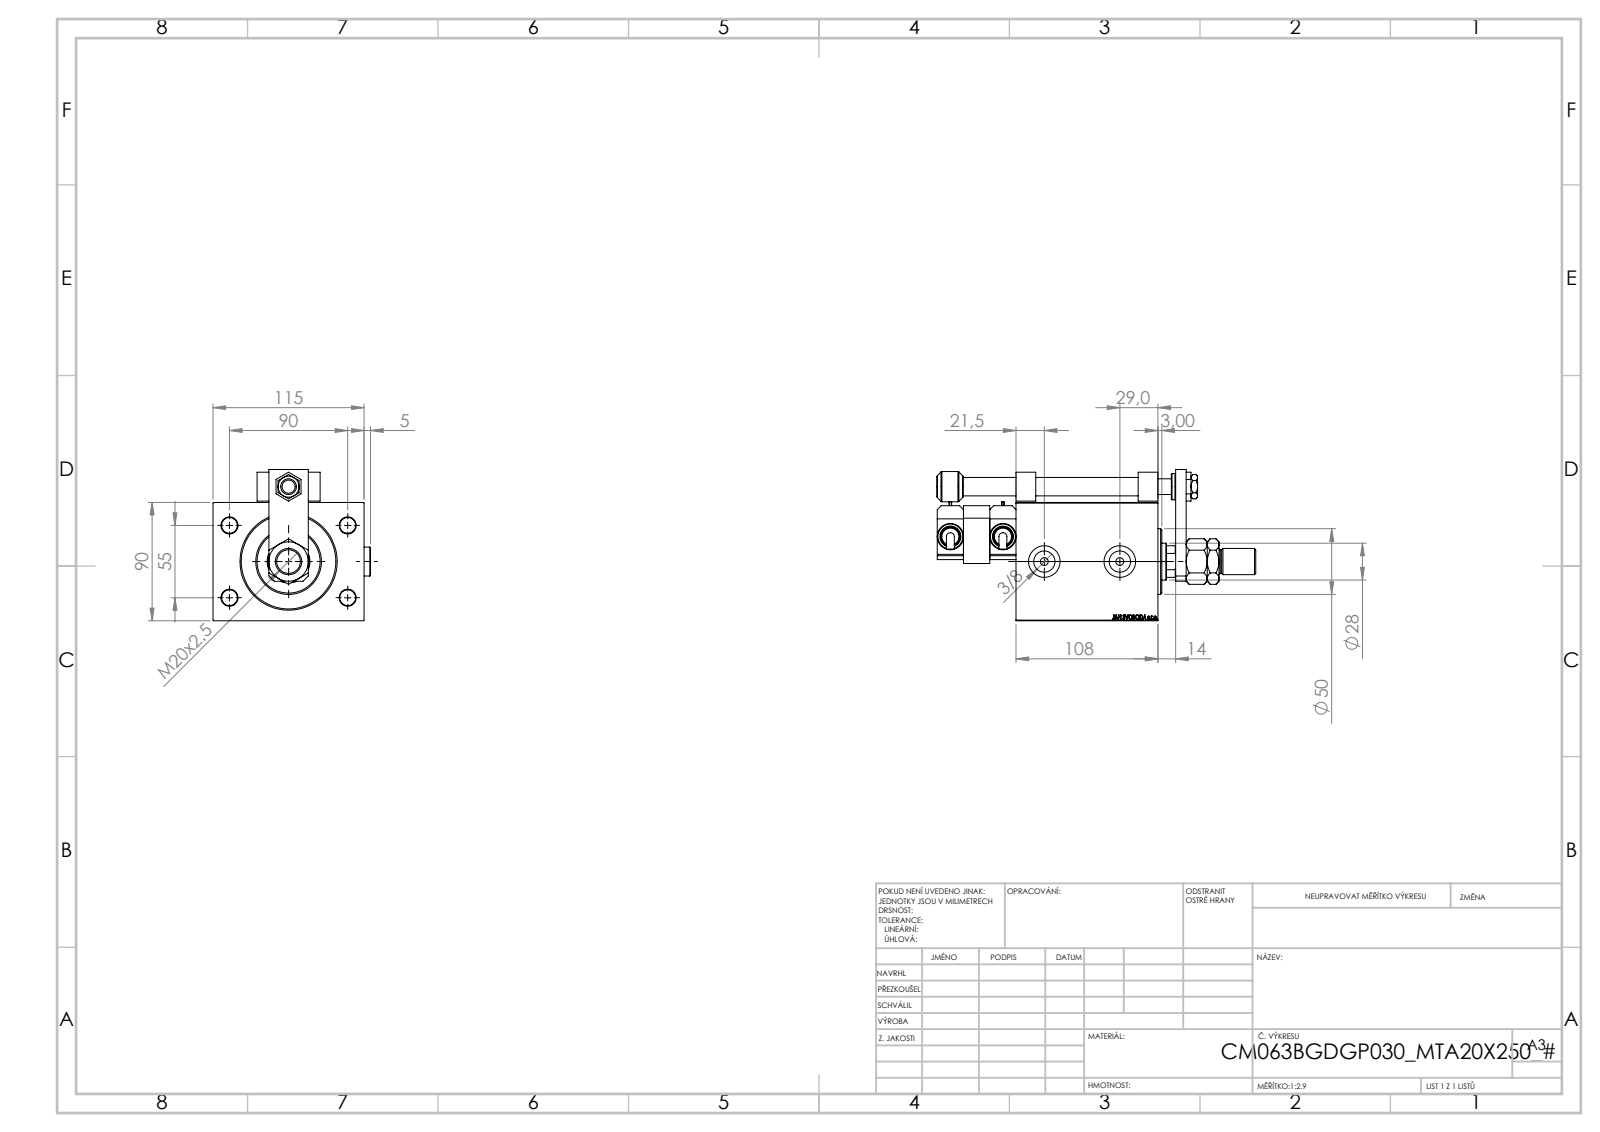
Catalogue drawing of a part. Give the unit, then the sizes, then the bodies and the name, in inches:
Units: inches
Overall size (bounding box): 9.559 × 4.72 × 4.528
Round holes (diameter × count): ⌀0.472 ×5, ⌀0.157 ×4, ⌀0.315 ×4, ⌀0.236 ×2, ⌀0.637 ×2, ⌀0.945 ×2, ⌀0.512 ×1, ⌀0.551 ×1, ⌀0.728 ×1, ⌀0.787 ×1, ⌀1.102 ×1, ⌀1.24 ×1
Round bosses / shafts (diameter × count): ⌀0.787 ×3, ⌀0.866 ×2, ⌀0.63 ×2, ⌀0.551 ×2, ⌀0.236 ×2, ⌀1.969 ×1, ⌀0.906 ×1, ⌀0.709 ×1
Partial cylindrical surfaces — rounded edges, fillets, slot ends (radius × count): R0.118 ×1, R0.531 ×1
Main face-to-face distances: 3.543, 4.528, 4.252, 0.787, 0.689, 1.476, 3.563, 1.378, 1.575, 0.531
Hole centre spacings: 2.076, 0.787, 2.119, 2.165, 3.543, 3.661, 3.745, 3.769
Volume: 74.57 in³ · Surface area: 286.5 in²
Bodies: 17 solids, 1212 faces (563 planar, 134 cylindrical, 515 other)
Part name (STEP PRODUCT): NUT_D16; Zatka_OIL_PORT; P_V_Z_MTA; SWITCH_P_FRONT_BACK (+7 more)
STEP written by: SolidWorks 2019 (CONFIG_CONTROL_DESIGN)
